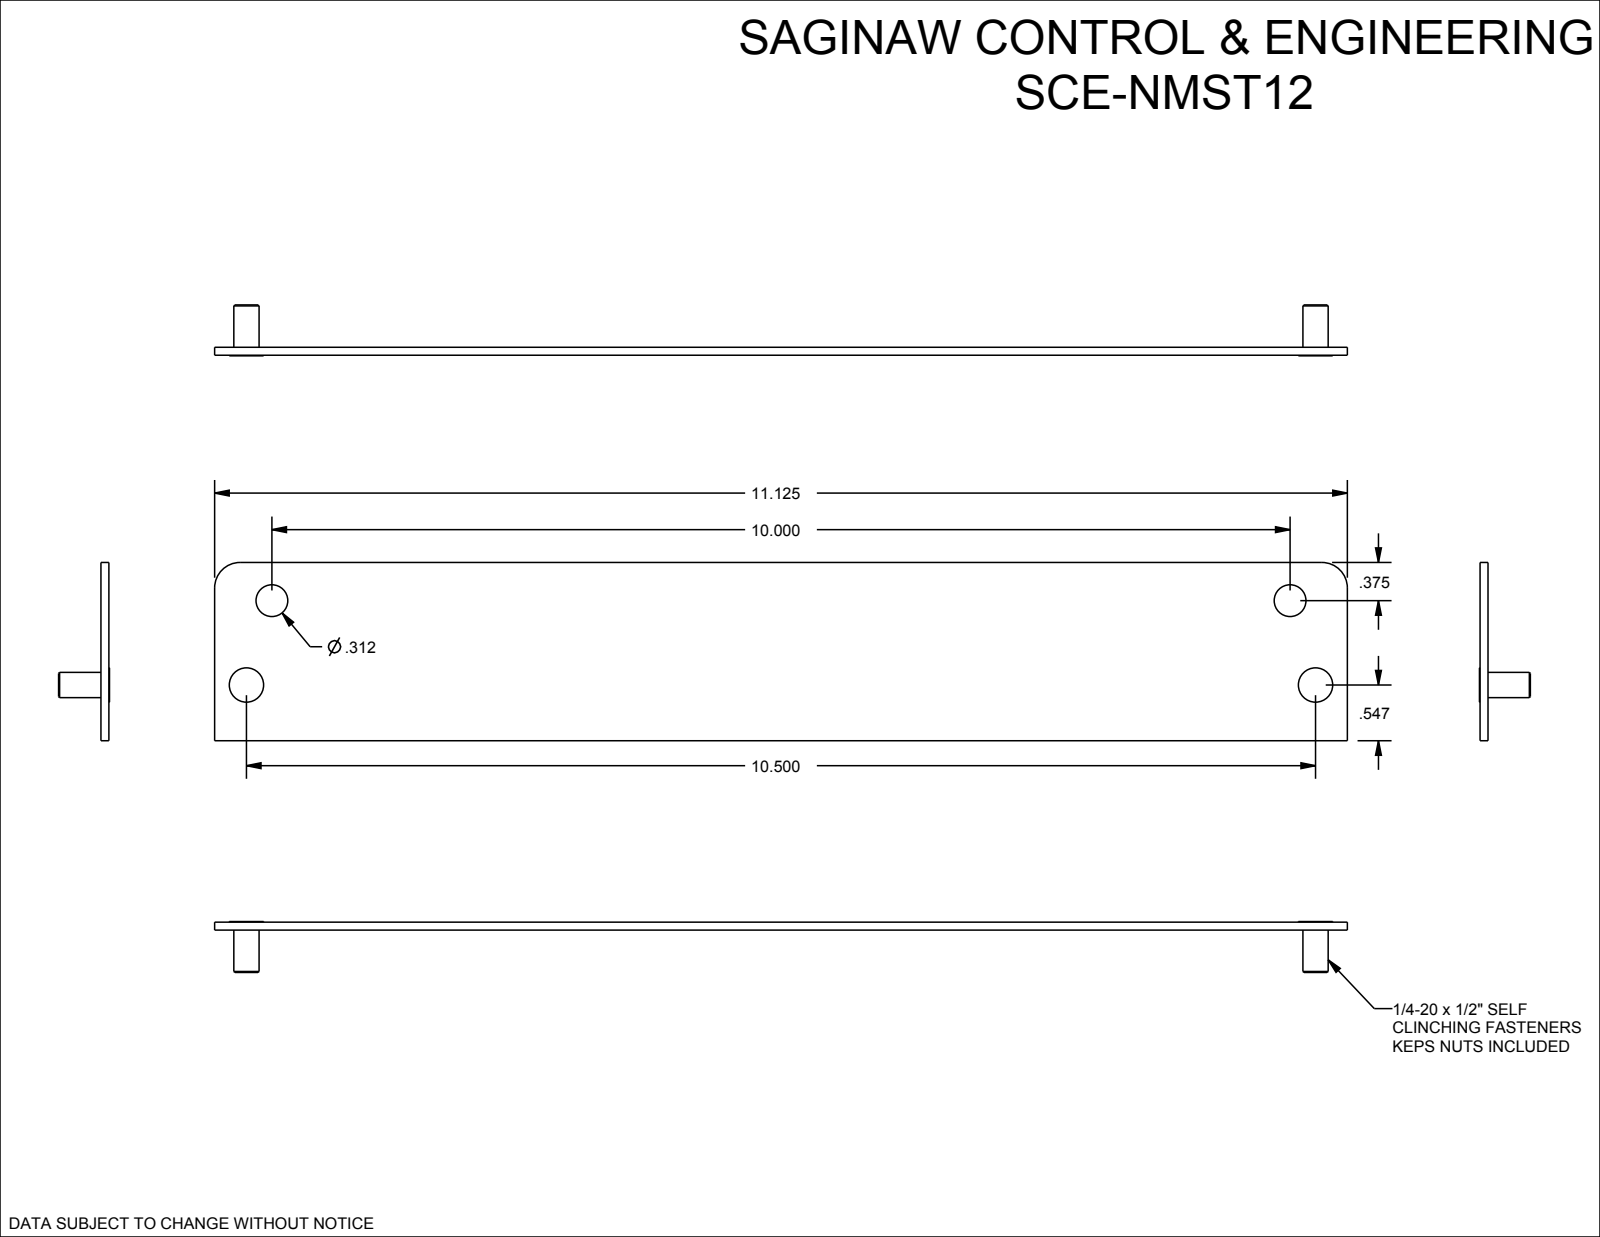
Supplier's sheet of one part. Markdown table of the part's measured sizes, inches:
| quantity | value |
| --- | --- |
| part name | SCE-NMST12 |
| STEP written by | SolidWorks 2019 (AUTOMOTIVE_DESIGN) |
| units | inches |
| bodies | 3 solids, 24 faces (12 planar, 10 cylindrical, 2 other) |
| overall size | 11.125 × 1.75 × 0.5 |
| volume | 1.547 in³ |
| surface area | 41.79 in² |
| round holes (diameter × count) | 0.25 × 2, 0.312 × 2 |
| round bosses / shafts (diameter × count) | 0.337 × 2, 0.248 × 2 |
| partial cylindrical surfaces (radius × count) | 0.25 × 2 |
| main face-to-face distances | 0.078, 1.75, 0.084, 11.125, 0.066, 0.018, 0.416, 0.482, 0.494, 0.5 |
| hole center spacings | 0.865, 10.283, 10, 10.5 |
